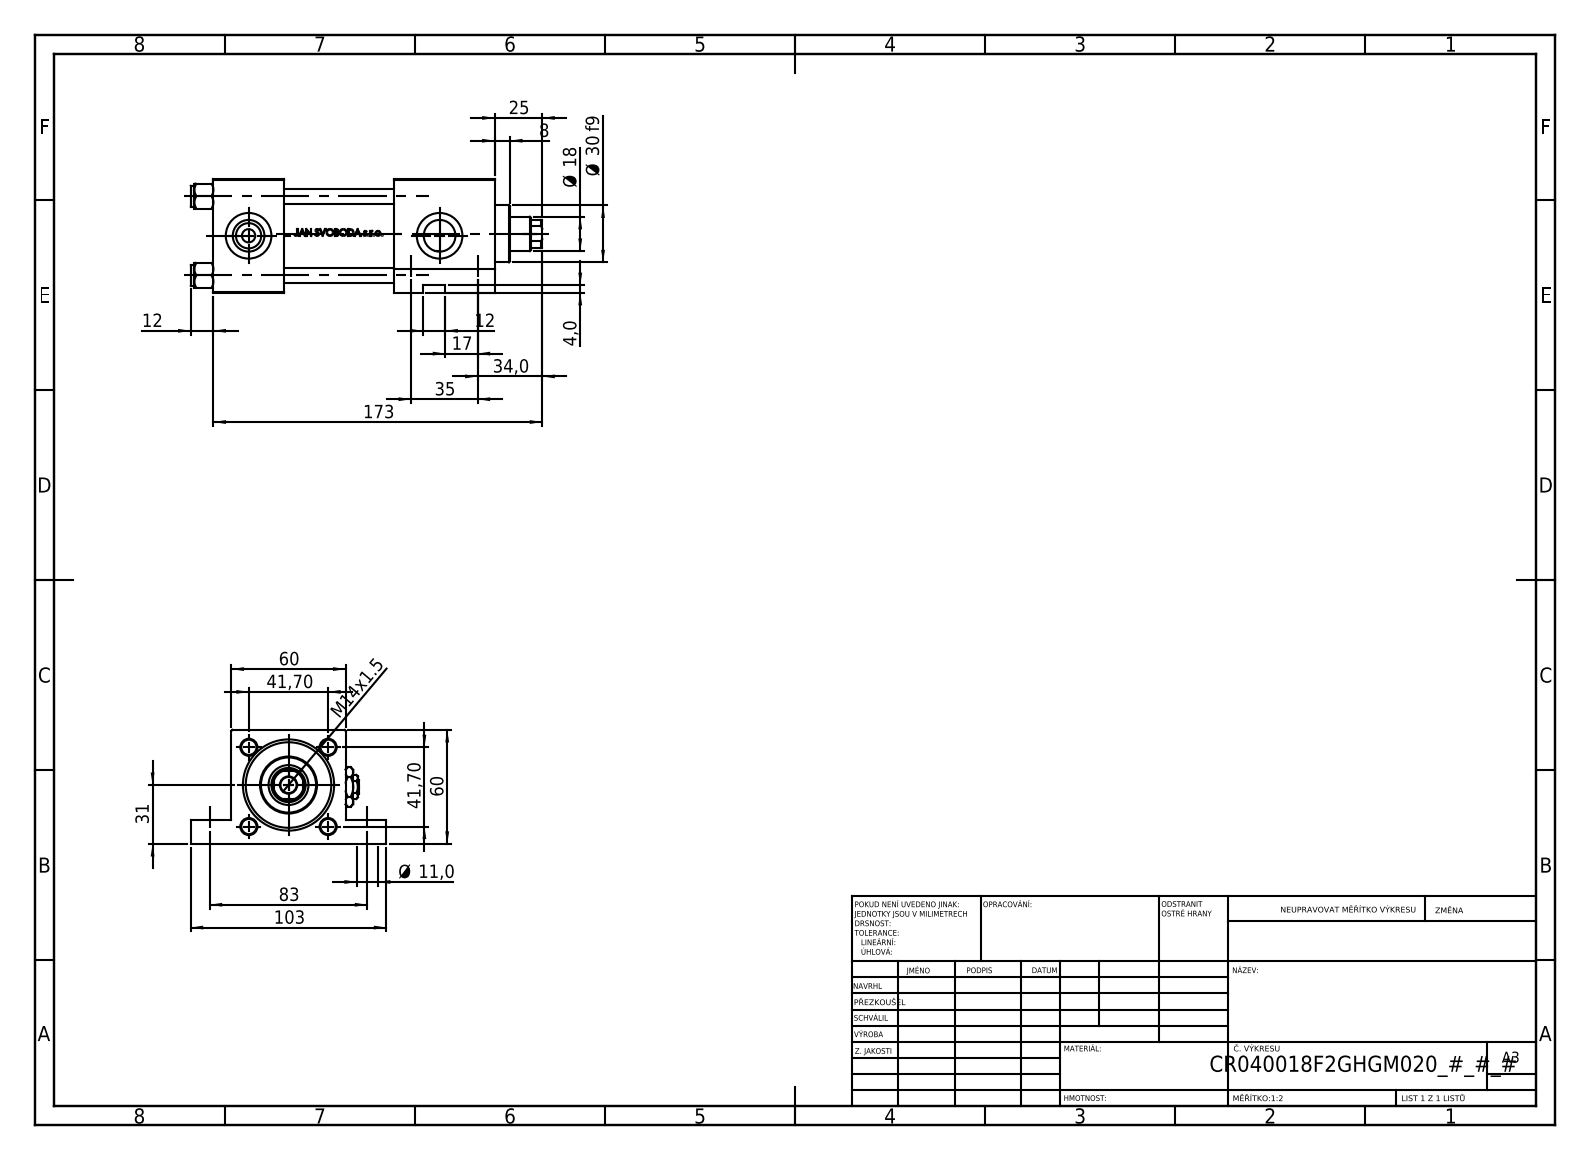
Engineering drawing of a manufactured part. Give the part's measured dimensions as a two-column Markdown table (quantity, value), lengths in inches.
| quantity | value |
| --- | --- |
| part name | NUT_M5_F; Zatka_pro_OIL_PORT; V215CR_VCP_F; V215CR_F_TYCINKA (+2 more) |
| STEP written by | SolidWorks 2019 (CONFIG_CONTROL_DESIGN) |
| units | inches |
| bodies | 12 solids, 1167 faces (460 planar, 145 cylindrical, 562 other) |
| overall size | 7.283 × 4.055 × 2.362 |
| volume | 25.75 in³ |
| surface area | 175.5 in² |
| round holes (diameter × count) | 0.315 × 4, 0.276 × 2, 0.433 × 2, 0.433 × 2, 0.656 × 2, 0.945 × 2, 0.335 × 1, 0.63 × 1, 0.709 × 1, 0.827 × 1, 1.22 × 1, 1.575 × 1 |
| round bosses / shafts (diameter × count) | 0.433 × 4, 1.811 × 1, 1.181 × 1 |
| partial cylindrical surfaces (radius × count) | 0.335 × 1 |
| main face-to-face distances | 2.362, 1.457, 5.827, 4.37, 2.283, 3.74, 2.087, 4.697, 3.24, 0.957 |
| hole center spacings | 1.642, 1.133, 1.189, 1.378, 2.322, 3.268, 3.546, 3.957 |
